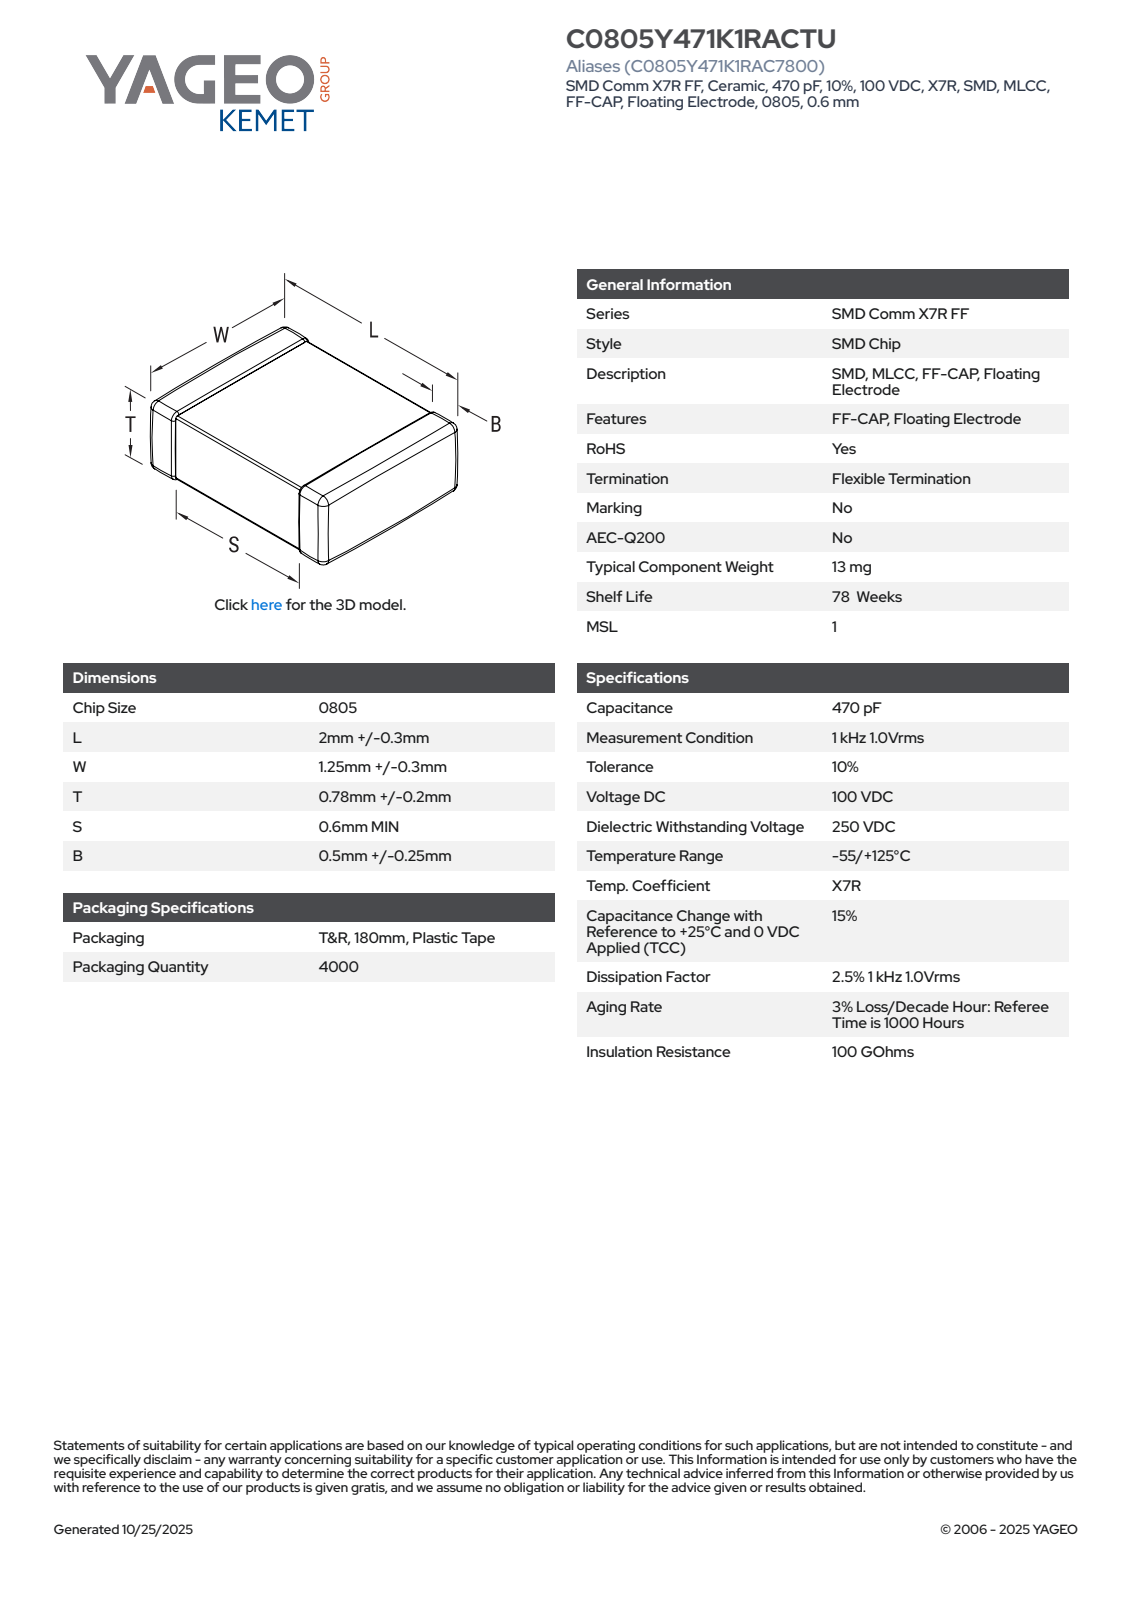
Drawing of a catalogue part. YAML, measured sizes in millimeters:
part_name: "CCS_CCSTD_0805_L2.3W1.55T0.98S0.6B0.75"
step_written_by: "SolidWorks 2021 (AUTOMOTIVE_DESIGN)"
units: millimeters
bodies: {solids: 4, faces: 121, planar: 71, cylindrical: 34, other: 16}
overall_size: [2.3, 1.55, 0.98]
volume: 3
surface_area: 15
face_to_face_distances: [0.95, 0.98, 1.52, 2.3, 1.55, 0.92, 1.49, 1.06, 1.24, 1.01]
